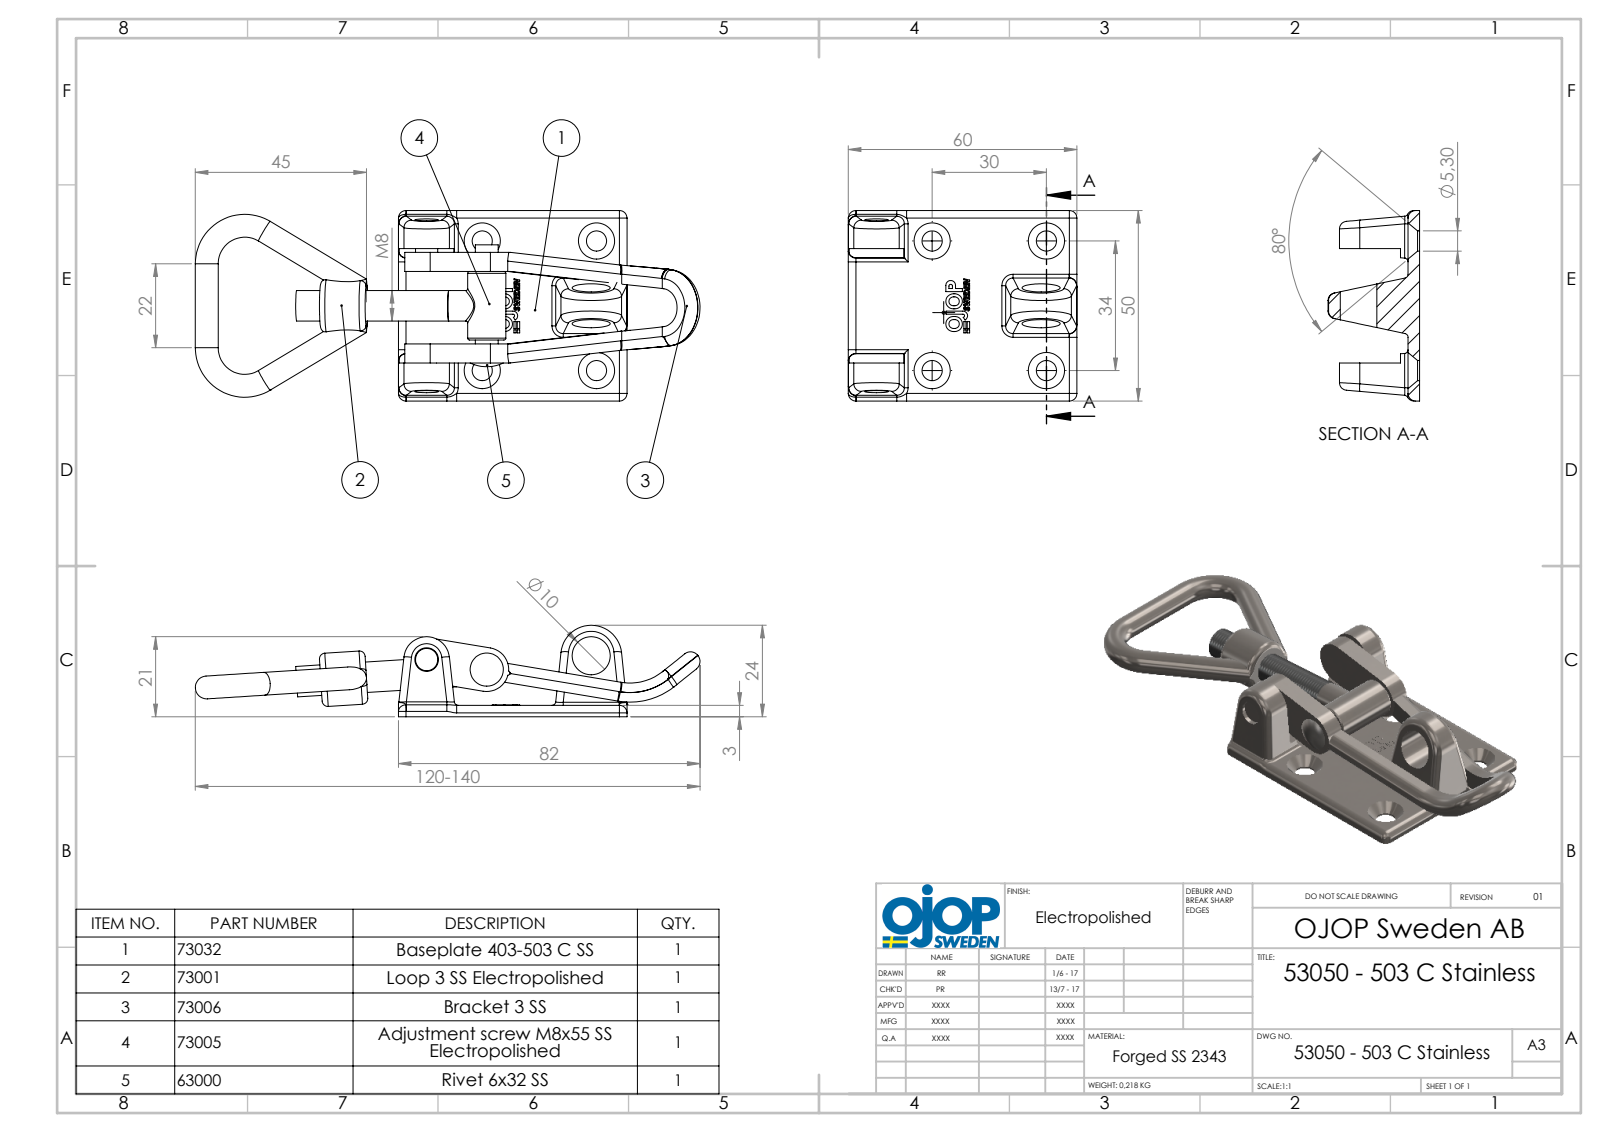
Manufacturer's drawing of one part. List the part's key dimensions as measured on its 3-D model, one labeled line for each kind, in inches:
Part name (STEP PRODUCT): 403-503 C; Justerskruv M8; Hålnit 6x32; 53050 - 503 C RF (+2 more)
STEP written by: SolidWorks 2015 (AUTOMOTIVE_DESIGN)
Units: inches
Bodies: 5 solids, 270 faces (60 planar, 105 cylindrical, 105 other)
Overall size (bounding box): 5.562 × 1.969 × 0.945
Volume: 1.741 in³ · Surface area: 29.37 in²
Round holes (diameter × count): ⌀0.209 ×4, ⌀0.244 ×2, ⌀0.118 ×1, ⌀0.248 ×1, ⌀0.319 ×1, ⌀0.394 ×1
Round bosses / shafts (diameter × count): ⌀0.236 ×4, ⌀0.394 ×1, ⌀0.315 ×1, ⌀0.315 ×1, ⌀0.23 ×1
Partial cylindrical surfaces — rounded edges, fillets, slot ends (radius × count): R0.079 ×30, R0.098 ×8, R0.275 ×4, R0.059 ×2, R0.242 ×2, R0.094 ×1, R0.197 ×1, R0.236 ×1
Main face-to-face distances: 0.118, 0.197, 0.984, 1.181, 0.787, 0.394, 0.591, 1.378, 1.575, 0.143
Hole centre spacings: 1.181, 1.339, 1.785, 0.63, 1.092, 1.701
